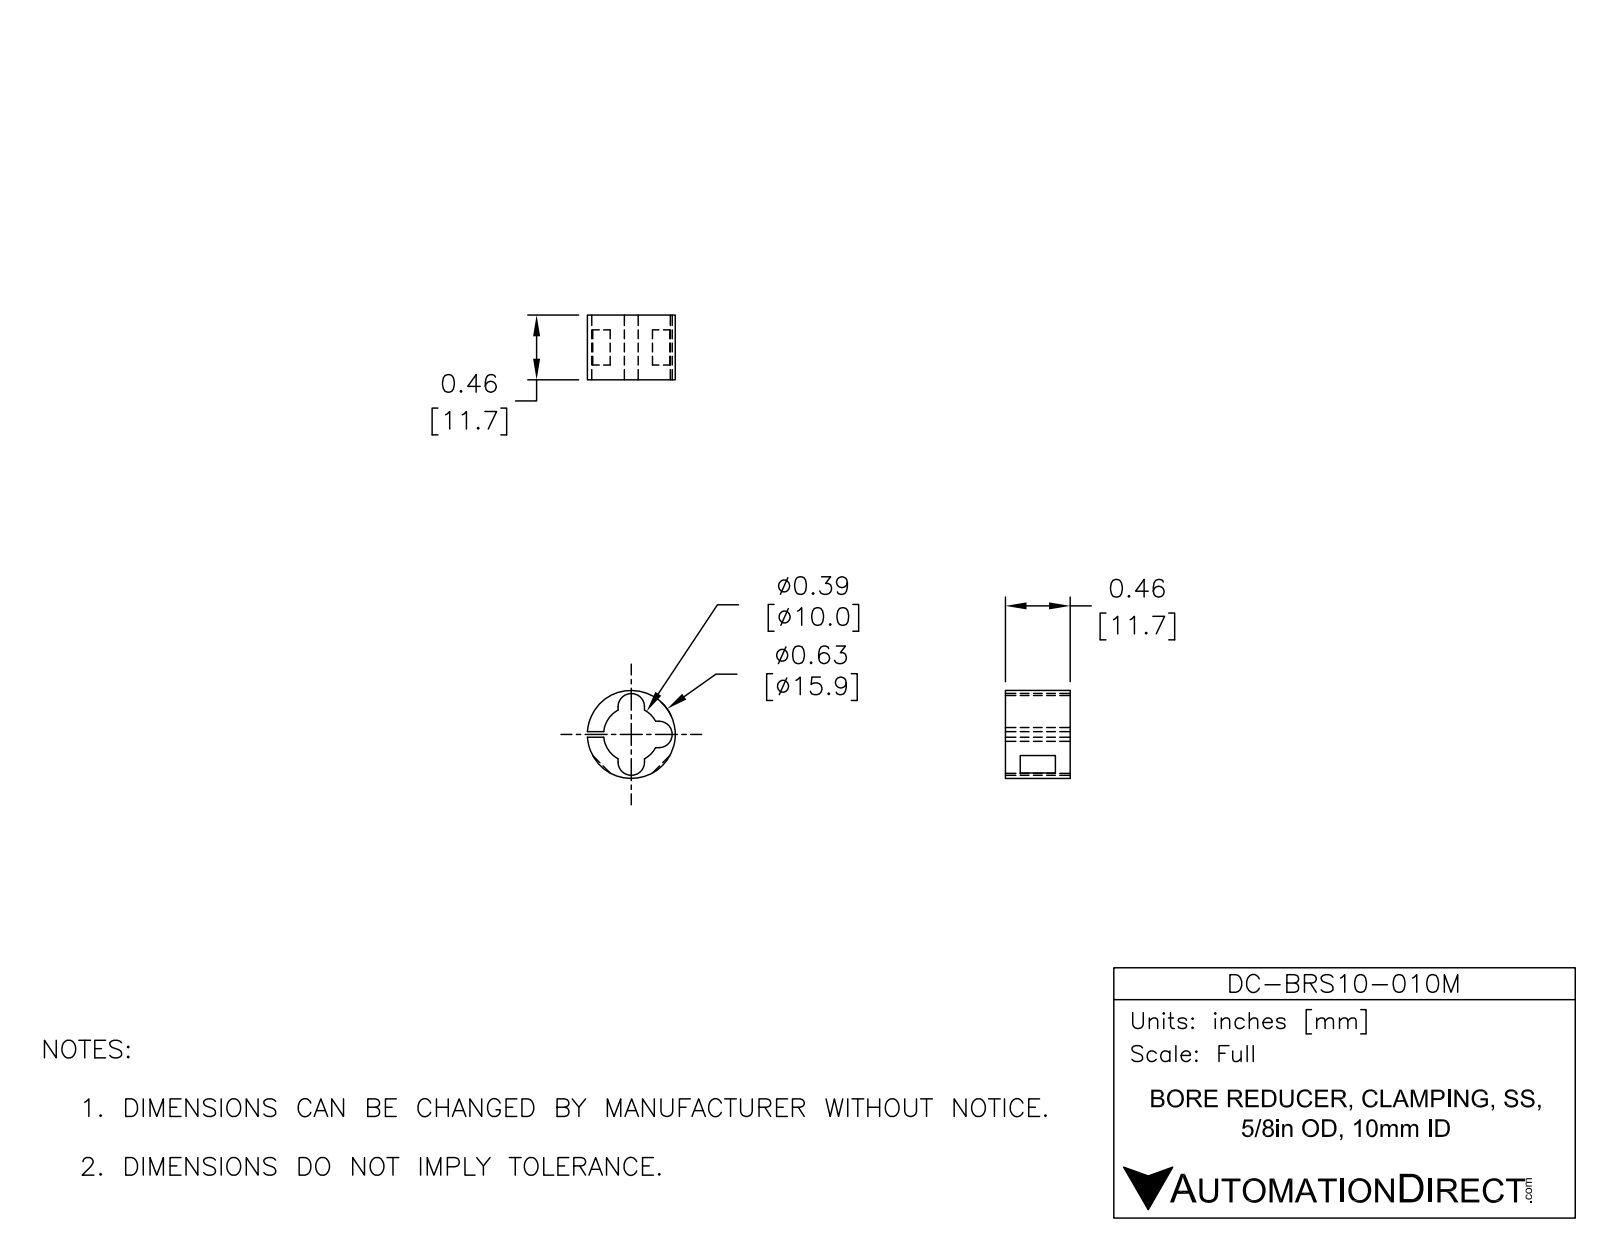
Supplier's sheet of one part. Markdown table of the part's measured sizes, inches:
| quantity | value |
| --- | --- |
| part name | DC-BRS10-10M |
| STEP written by | SolidWorks 2015 (AUTOMOTIVE_DESIGN) |
| units | inches |
| bodies | 1 solid, 27 faces (16 planar, 11 cylindrical, 0 other) |
| overall size | 0.625 × 0.624 × 0.46 |
| volume | 0.061 in³ |
| surface area | 2.018 in² |
| round bosses / shafts (diameter × count) | 0.625 × 1 |
| partial cylindrical surfaces (radius × count) | 0.094 × 3, 0.197 × 1 |
| main face-to-face distances | 0.46, 0.04, 0.187, 0.074, 0.114, 0.105, 0.355, 0.25 |
